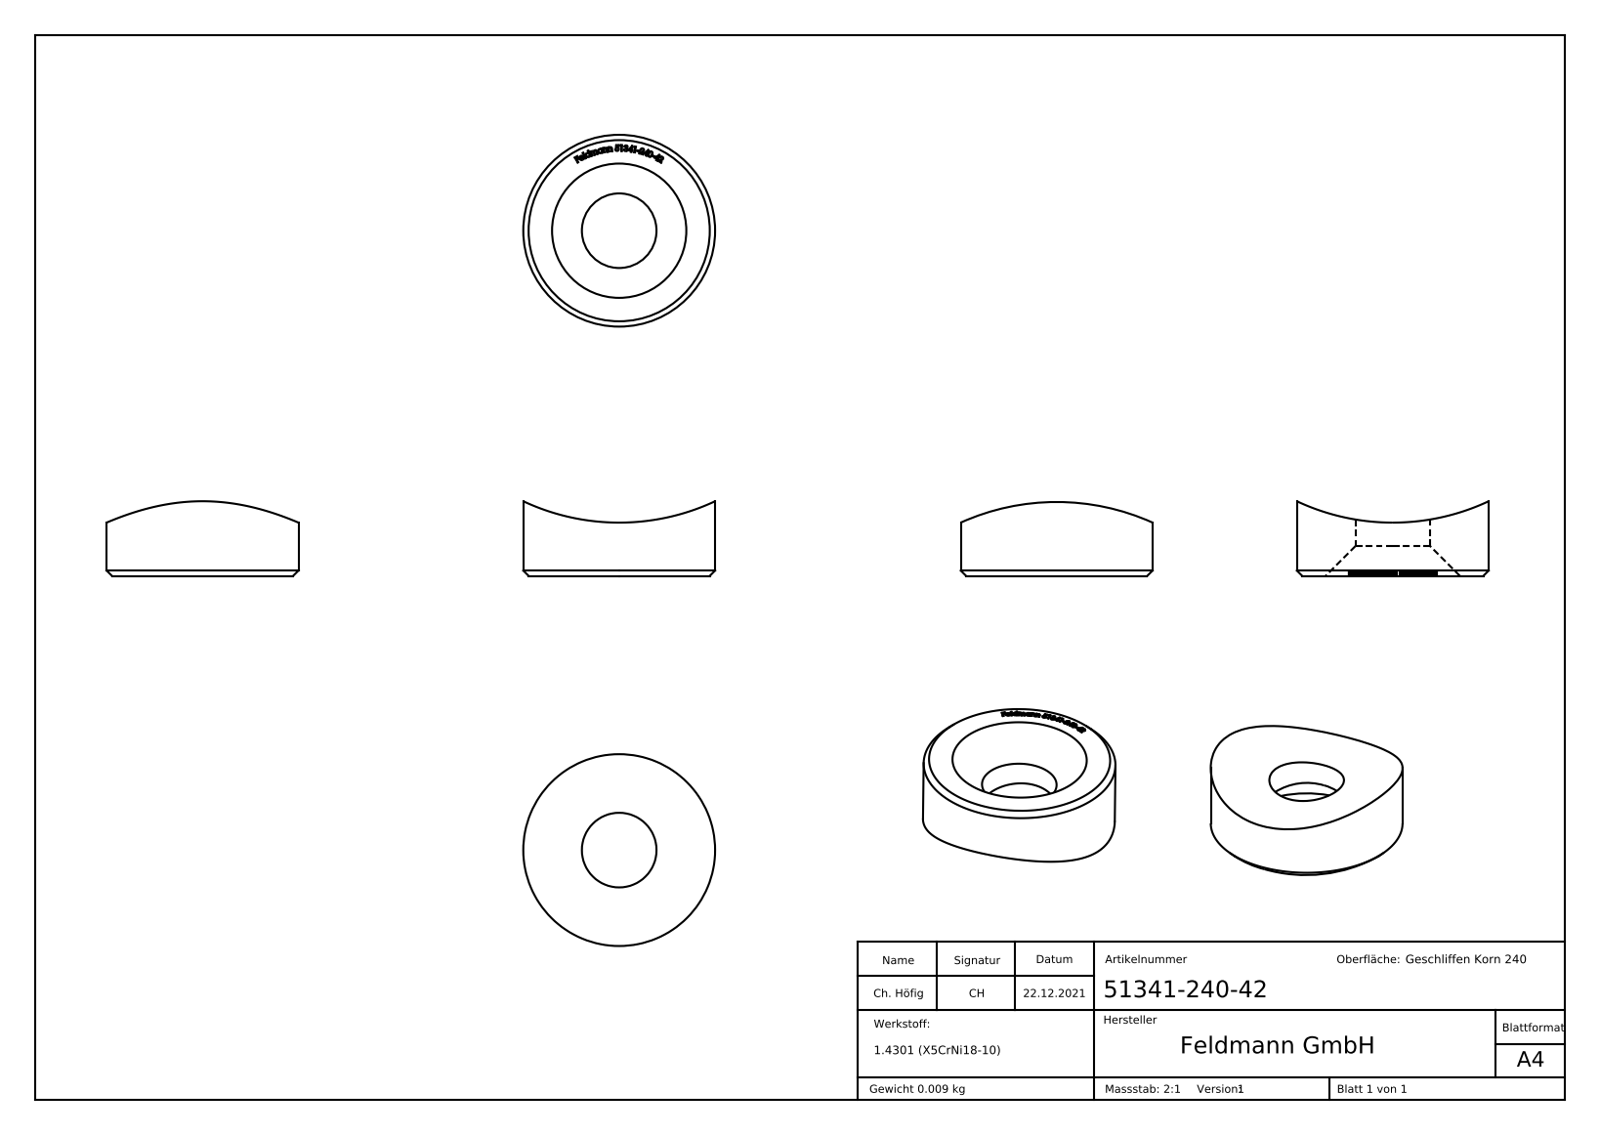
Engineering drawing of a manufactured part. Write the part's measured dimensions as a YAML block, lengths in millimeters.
part_name: "51341-240-42"
step_written_by: "SolidWorks 2018 (CONFIG_CONTROL_DESIGN)"
units: millimeters
bodies: {solids: 1, faces: 262, planar: 162, cylindrical: 5, other: 95}
overall_size: [18, 18, 7]
volume: 1085
surface_area: 868
round_holes:
  - {diameter: 7, count: 1}
round_bosses_or_shafts:
  - {diameter: 18, count: 1}
partial_cylinders:
  - {radius: 21.2, count: 1}
face_to_face_distances: [0.5, 0.34, 0.32, 0.39, 0.53, 0.48, 0.54, 0.35, 0.36, 0.38]
